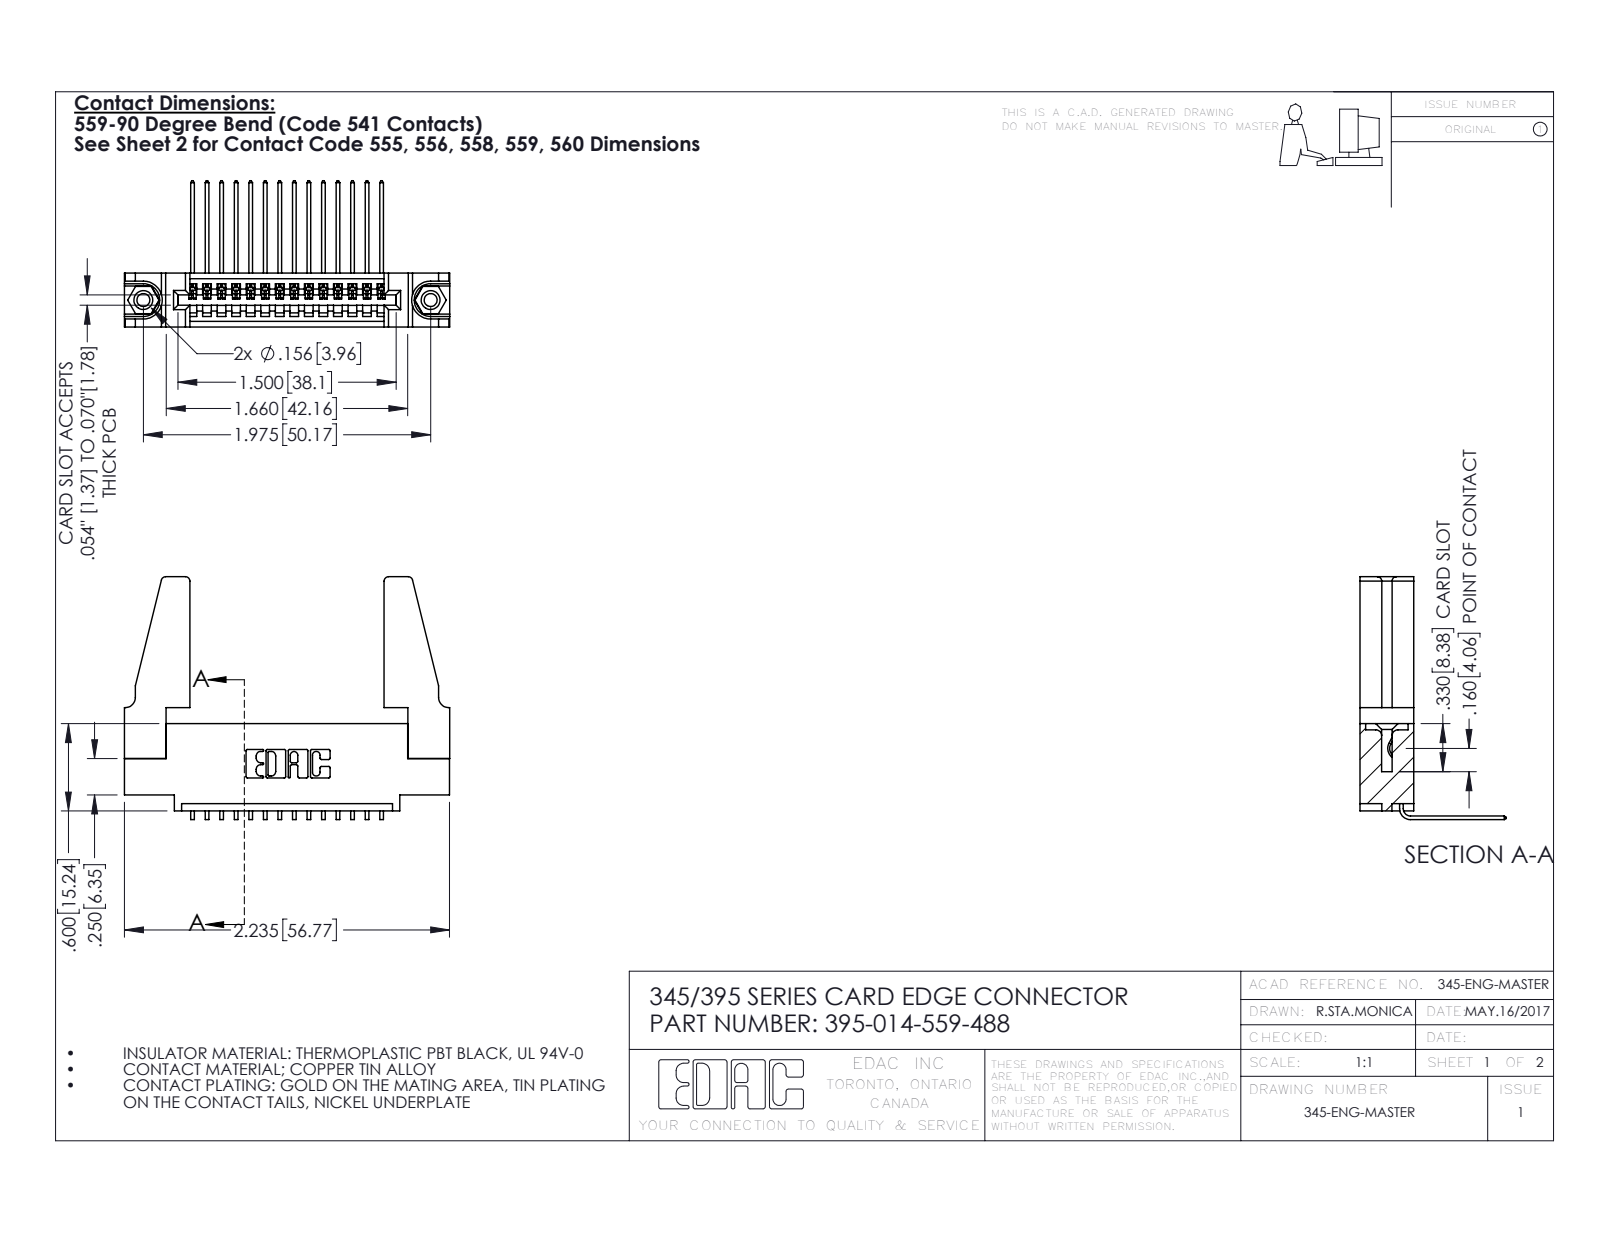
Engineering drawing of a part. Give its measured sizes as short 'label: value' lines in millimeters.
name: 395-014-559-488; 345-292-001_558 559 Tail - 1; 345-220-078_345-220-088; 345-250-001_345-250-001-102 (+1 more)
written by: SolidWorks 2016 (CONFIG_CONTROL_DESIGN)
unit: mm
bodies: 19 solids, 1094 faces (744 planar, 334 cylindrical, 16 other)
size: 56.8 × 42.4 × 25.5
volume: 8 390 mm³; area: 9 935 mm²
holes: 2× ⌀2.3, 2× ⌀3.2, 2× ⌀4, 1× ⌀1.6
bosses: 2× ⌀3.9
rounds: 28× R0.2, 22× R0.3, 8× R0.8, 6× R0.2, 6× R0.8, 3× R0.7, 2× R0.8, 2× R1
face distances: 9.4, 1.8, 7.6, 5.1, 2.5, 6.9, 0.6, 5.7, 3.8, 3.8
hole spacings: 6.9, 44.2, 50.2
